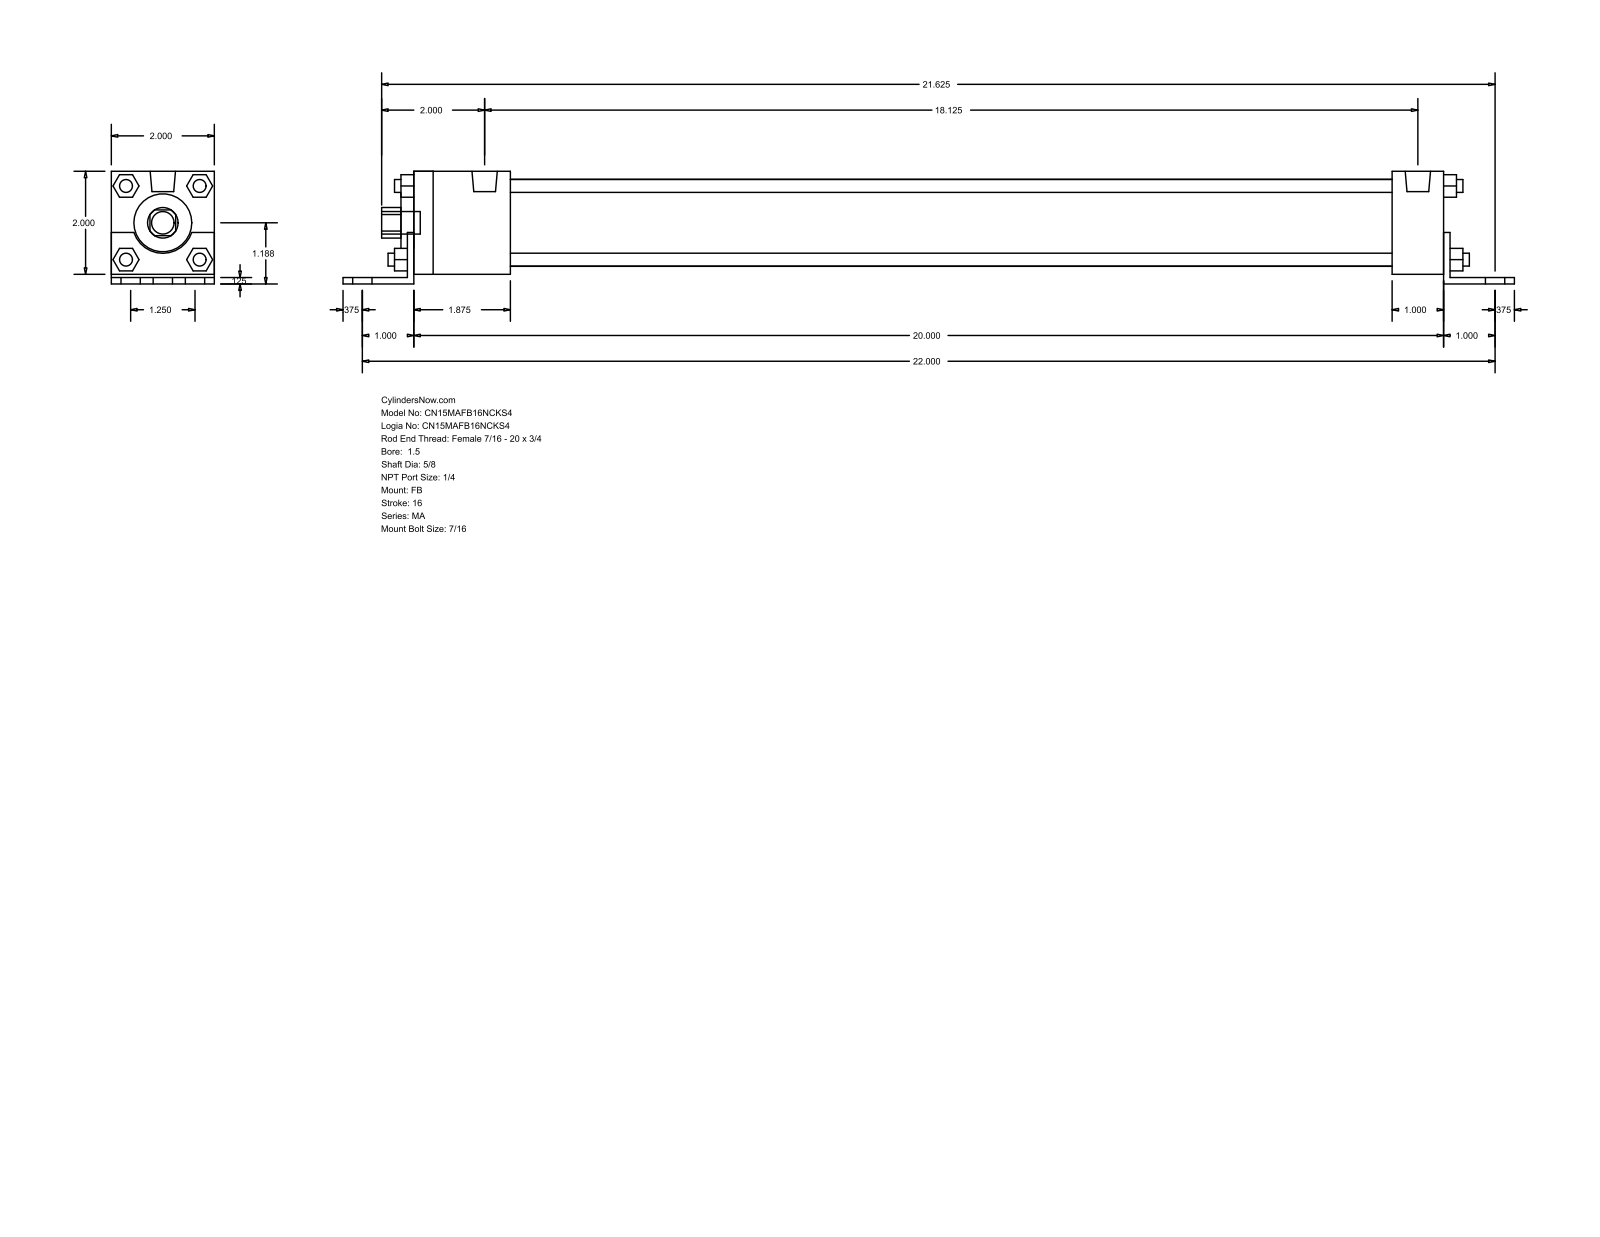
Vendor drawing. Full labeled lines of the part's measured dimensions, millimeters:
Part name (STEP PRODUCT): MA_FB__0150_0.625
STEP written by: GSSL Pune (CONFIG_CONTROL_DESIGN)
Units: millimetres
Bodies: 0 solids, 140 faces (105 planar, 35 cylindrical, 0 other)
Overall size (bounding box): 577.85 × 55.56 × 50.8
Round holes (diameter × count): ⌀15.88 ×1, ⌀28.57 ×1, ⌀42.93 ×1
Round bosses / shafts (diameter × count): ⌀11.11 ×7, ⌀7.94 ×4, ⌀6.35 ×4, ⌀12.49 ×2
Partial cylindrical surfaces — rounded edges, fillets, slot ends (radius × count): R7.54 ×1, R15.05 ×1
Main face-to-face distances: 50.8, 3.17, 4.76, 55.56, 1.59, 52.39, 25.4, 514.35, 6.35, 3.18
